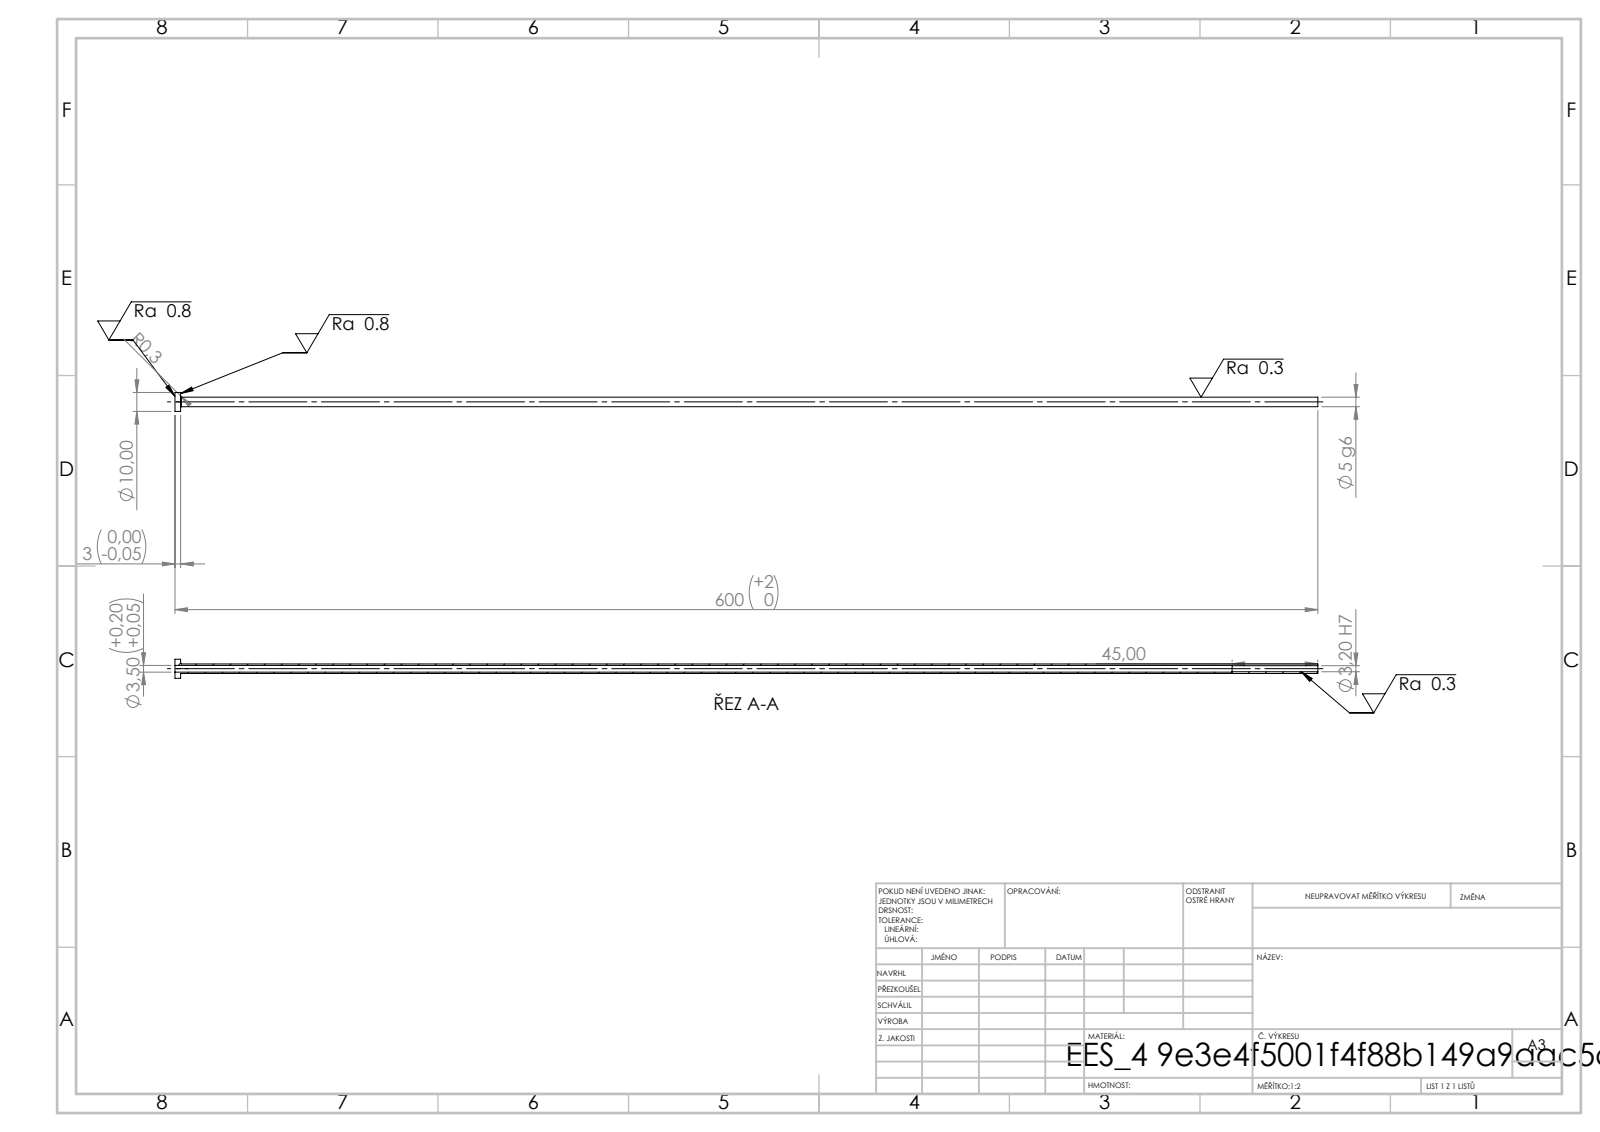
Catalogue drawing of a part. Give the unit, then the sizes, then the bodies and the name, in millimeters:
Units: millimetres
Overall size (bounding box): 600 × 10 × 10
Round holes (diameter × count): ⌀3.2 ×1, ⌀3.5 ×1
Round bosses / shafts (diameter × count): ⌀10 ×1, ⌀5 ×1
Main face-to-face distances: 3, 600, 597, 555, 552, 45
Volume: 6 256 mm³ · Surface area: 16 166 mm²
Bodies: 1 solid, 14 faces (4 planar, 8 cylindrical, 2 other)
STEP written by: SolidWorks 2019 (CONFIG_CONTROL_DESIGN)
